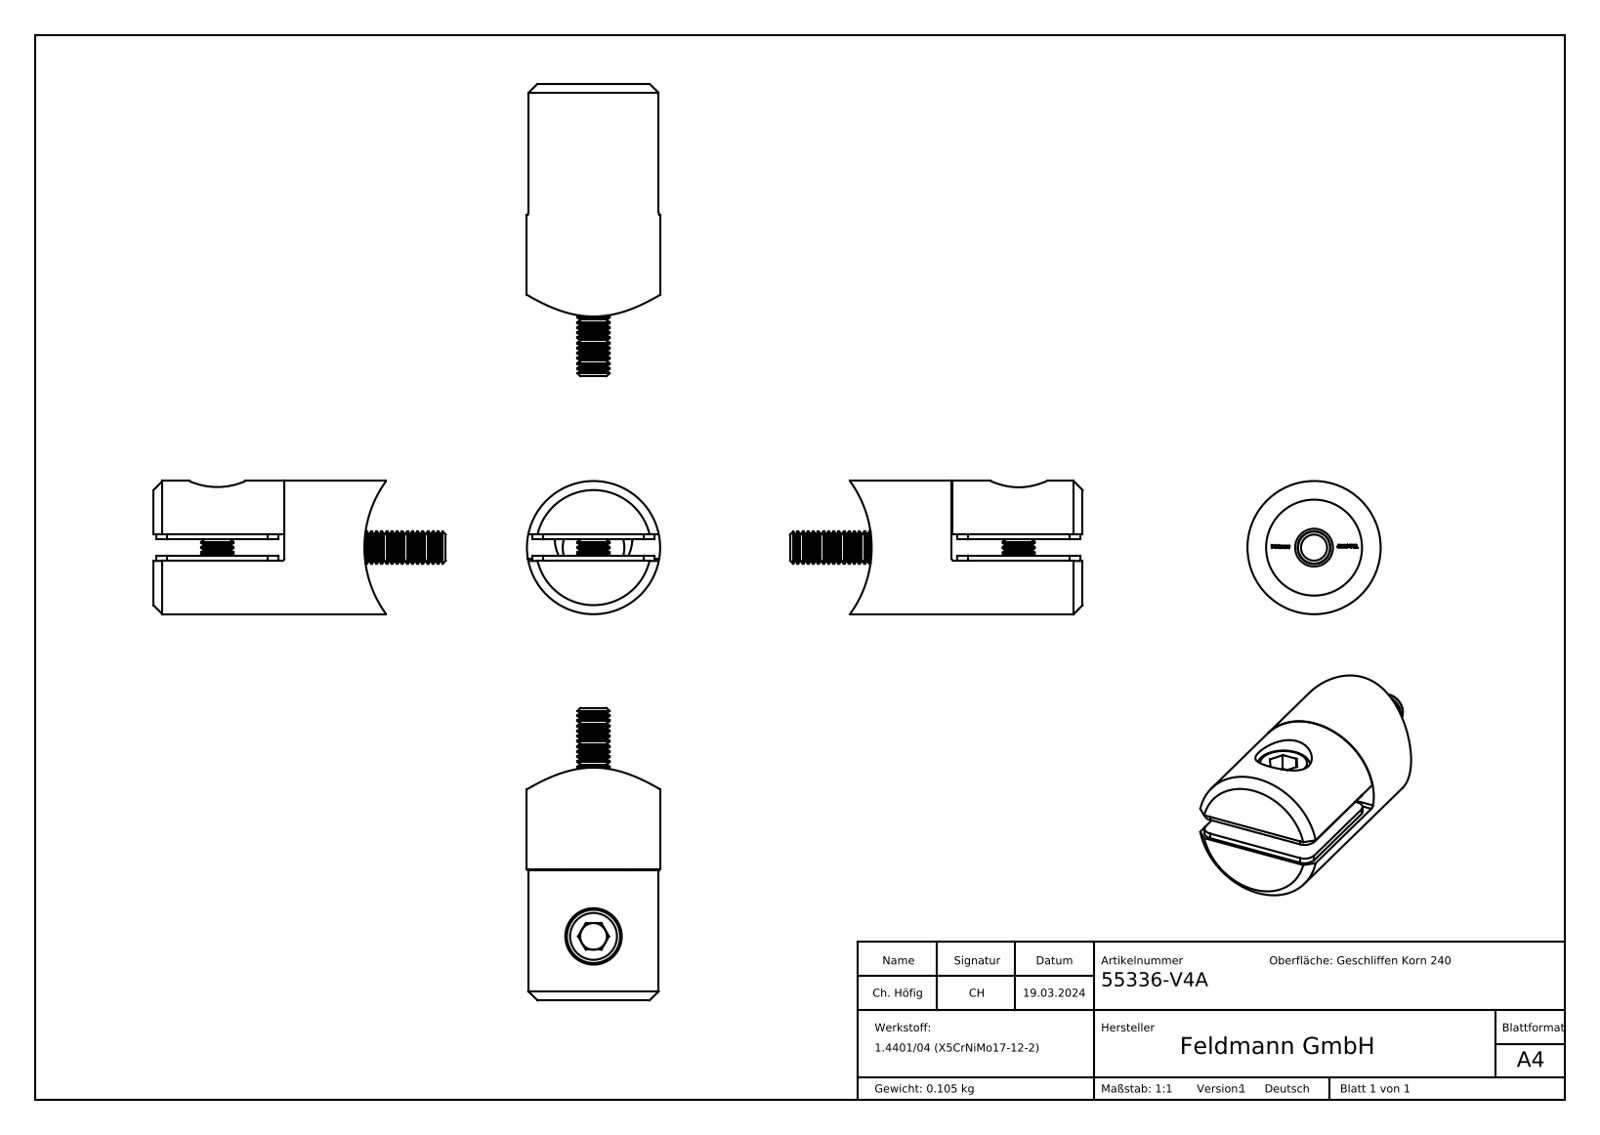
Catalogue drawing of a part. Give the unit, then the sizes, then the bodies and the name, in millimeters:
Units: millimetres
Overall size (bounding box): 54.88 × 25 × 25
Round holes (diameter × count): ⌀4 ×2, ⌀5 ×1, ⌀6.5 ×1, ⌀7 ×1, ⌀7.1 ×1, ⌀10.58 ×1, ⌀14.6 ×1, ⌀18 ×1
Round bosses / shafts (diameter × count): ⌀6 ×2, ⌀25 ×1, ⌀11.57 ×1, ⌀10 ×1
Partial cylindrical surfaces — rounded edges, fillets, slot ends (radius × count): R0.2 ×40, R2 ×6, R1.25 ×2, R0.5 ×1, R21.2 ×1
Main face-to-face distances: 4, 1, 5, 3, 34.5, 10, 24.5, 6, 9.9, 24.6
Hole centre spacings: 9.37, 12
Volume: 15 433 mm³ · Surface area: 10 554 mm²
Bodies: 6 solids, 712 faces (225 planar, 187 cylindrical, 300 other)
Part name (STEP PRODUCT): 5533X-240 Teil1_55336-V4A Teil1; 55336-V4A; socket countersunk head screw_din_DIN 7991 - M6 x 25 --- 25S; 5533X-240 Teil2_5533X-240 Teil2 (+2 more)
STEP written by: SolidWorks 2018 (CONFIG_CONTROL_DESIGN)
